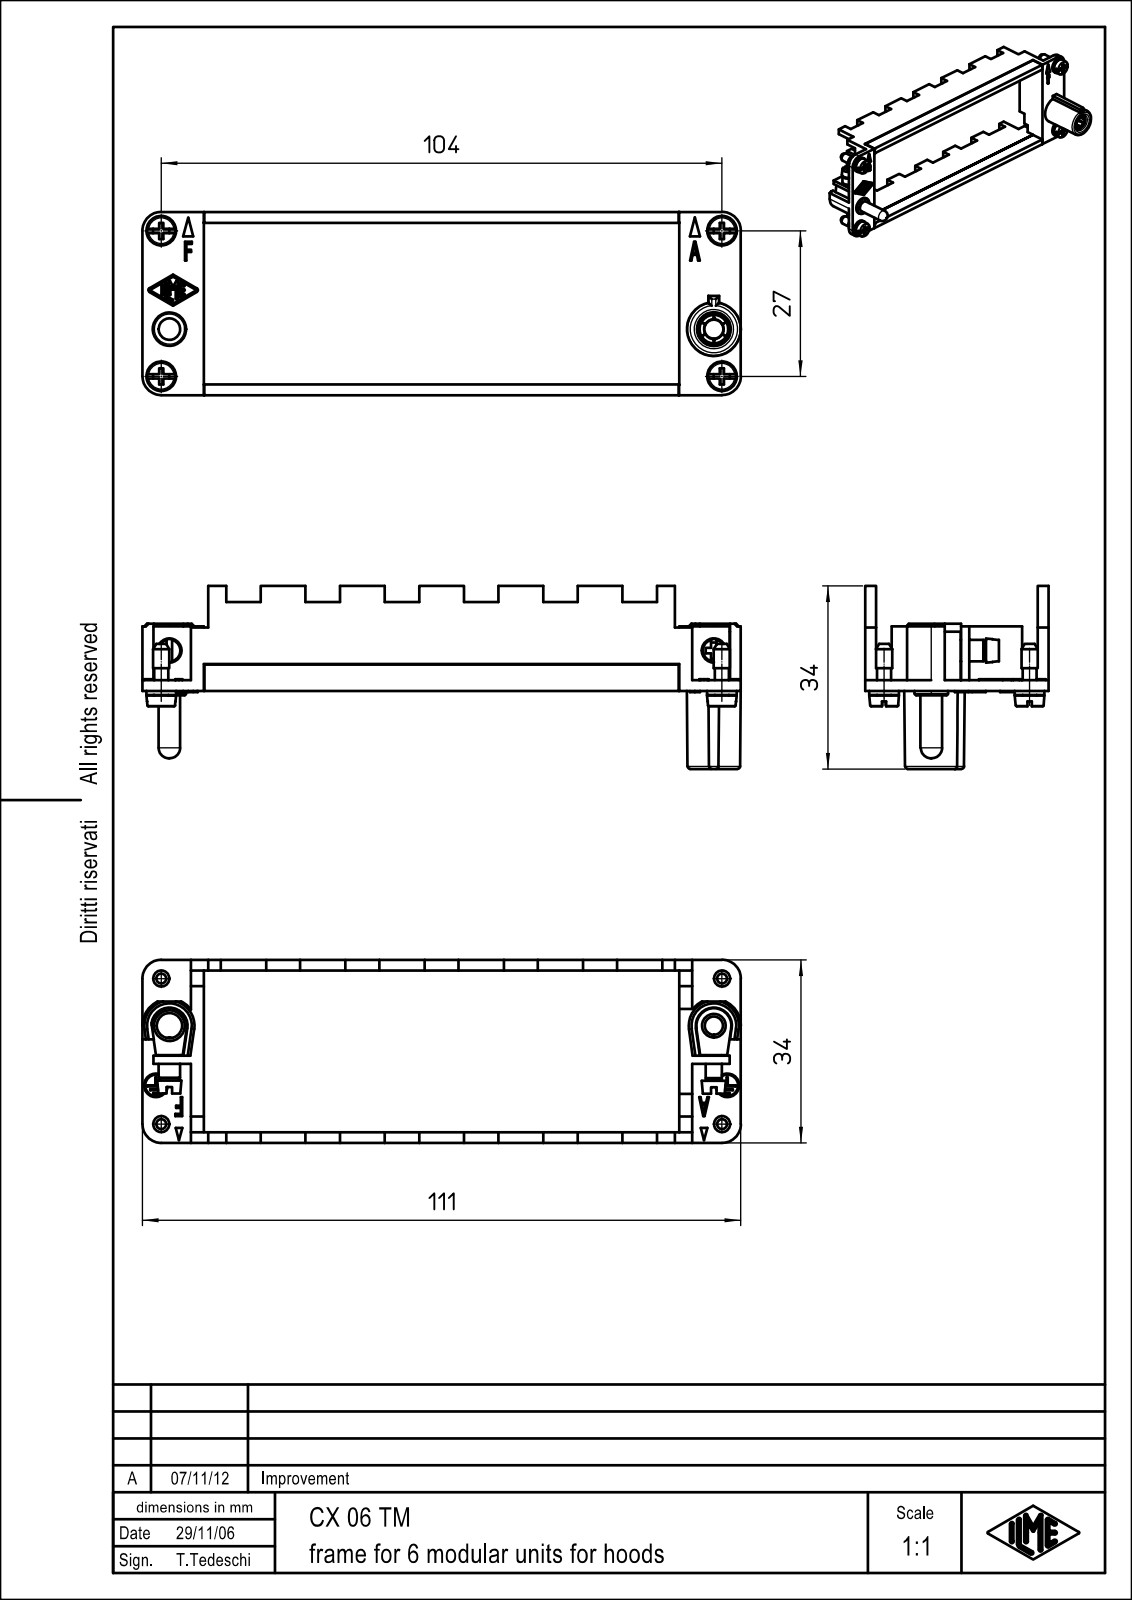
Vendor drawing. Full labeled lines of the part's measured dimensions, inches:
Part name (STEP PRODUCT): CX_06_TM
STEP written by: Creo Elements/Direct Modeling 18.0B 02-Dec-2011 (C) Parametric Technology GmbH (AUTOMOTIVE_DESIGN)
Units: inches
Bodies: 1 solid, 651 faces (455 planar, 104 cylindrical, 92 other)
Overall size (bounding box): 4.37 × 1.339 × 1.339
Volume: 0.748 in³ · Surface area: 22.07 in²
Round holes (diameter × count): ⌀0.157 ×2, ⌀0.098 ×1, ⌀0.13 ×1, ⌀0.134 ×1, ⌀0.165 ×1, ⌀0.185 ×1, ⌀0.248 ×1
Round bosses / shafts (diameter × count): ⌀0.118 ×5, ⌀0.217 ×4, ⌀0.102 ×4, ⌀0.173 ×2, ⌀0.157 ×2, ⌀0.244 ×1, ⌀0.236 ×1, ⌀0.138 ×1
Partial cylindrical surfaces — rounded edges, fillets, slot ends (radius × count): R0.007 ×11, R0.138 ×4, R0.02 ×3, R0.005 ×2, R0.016 ×2, R0.128 ×2, R0.132 ×2, R0.197 ×2
Main face-to-face distances: 0.079, 1.26, 1.339, 1.181, 0.094, 3.567, 3.472, 0.118, 0.571, 0.354
Hole centre spacings: 0.446, 3.976, 4.098, 4.098, 4.174
